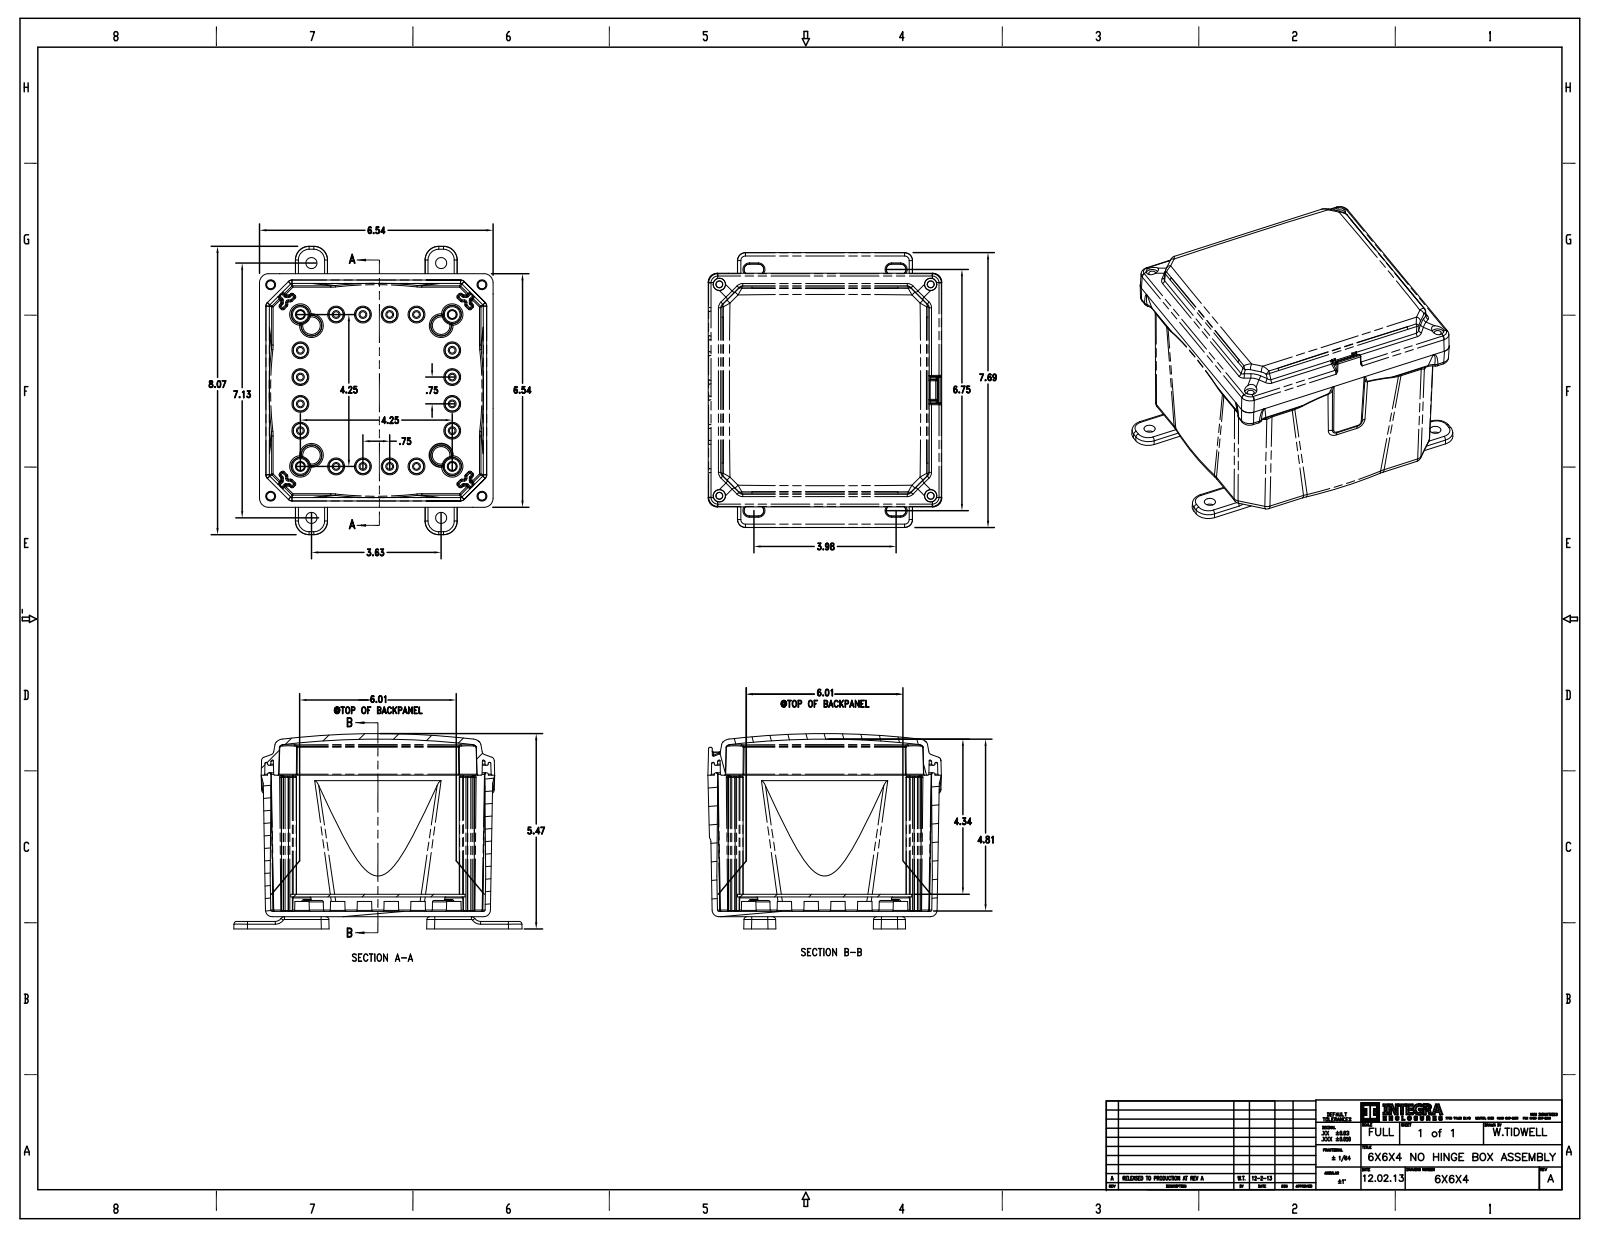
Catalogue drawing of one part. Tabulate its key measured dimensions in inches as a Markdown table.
| quantity | value |
| --- | --- |
| part name | H664BS; 9912525-80-10; 9912521-80-10; H664BS_ASM (+5 more) |
| STEP written by | CREO PARAMETRIC BY PTC INC, 2016050 (CONFIG_CONTROL_DESIGN) |
| units | inches |
| bodies | 24 solids, 3400 faces (754 planar, 1367 cylindrical, 1279 other) |
| overall size | 7.69 × 6.536 × 5.465 |
| volume | 38.05 in³ |
| surface area | 526.9 in² |
| round holes (diameter × count) | 0.16 × 16, 0.19 × 8, 0.201 × 4 |
| round bosses / shafts (diameter × count) | 0.25 × 12, 0.3 × 8, 0.298 × 8, 0.29 × 8, 0.26 × 8, 0.258 × 8, 0.375 × 4, 0.372 × 4 |
| partial cylindrical surfaces (radius × count) | 0.03 × 349, 0.02 × 88, 0.025 × 60, 0.005 × 48, 0.09 × 36, 0.1 × 28, 0.08 × 26, 0.2 × 24 |
| main face-to-face distances | 0.15, 0.49, 0.12, 3.81, 0.34, 3.96, 0.392, 0.22, 4.3, 6.184 |
| hole center spacings | 4.25, 4.315, 4.596, 0.75, 0.757, 1, 1.473, 1.5 |
